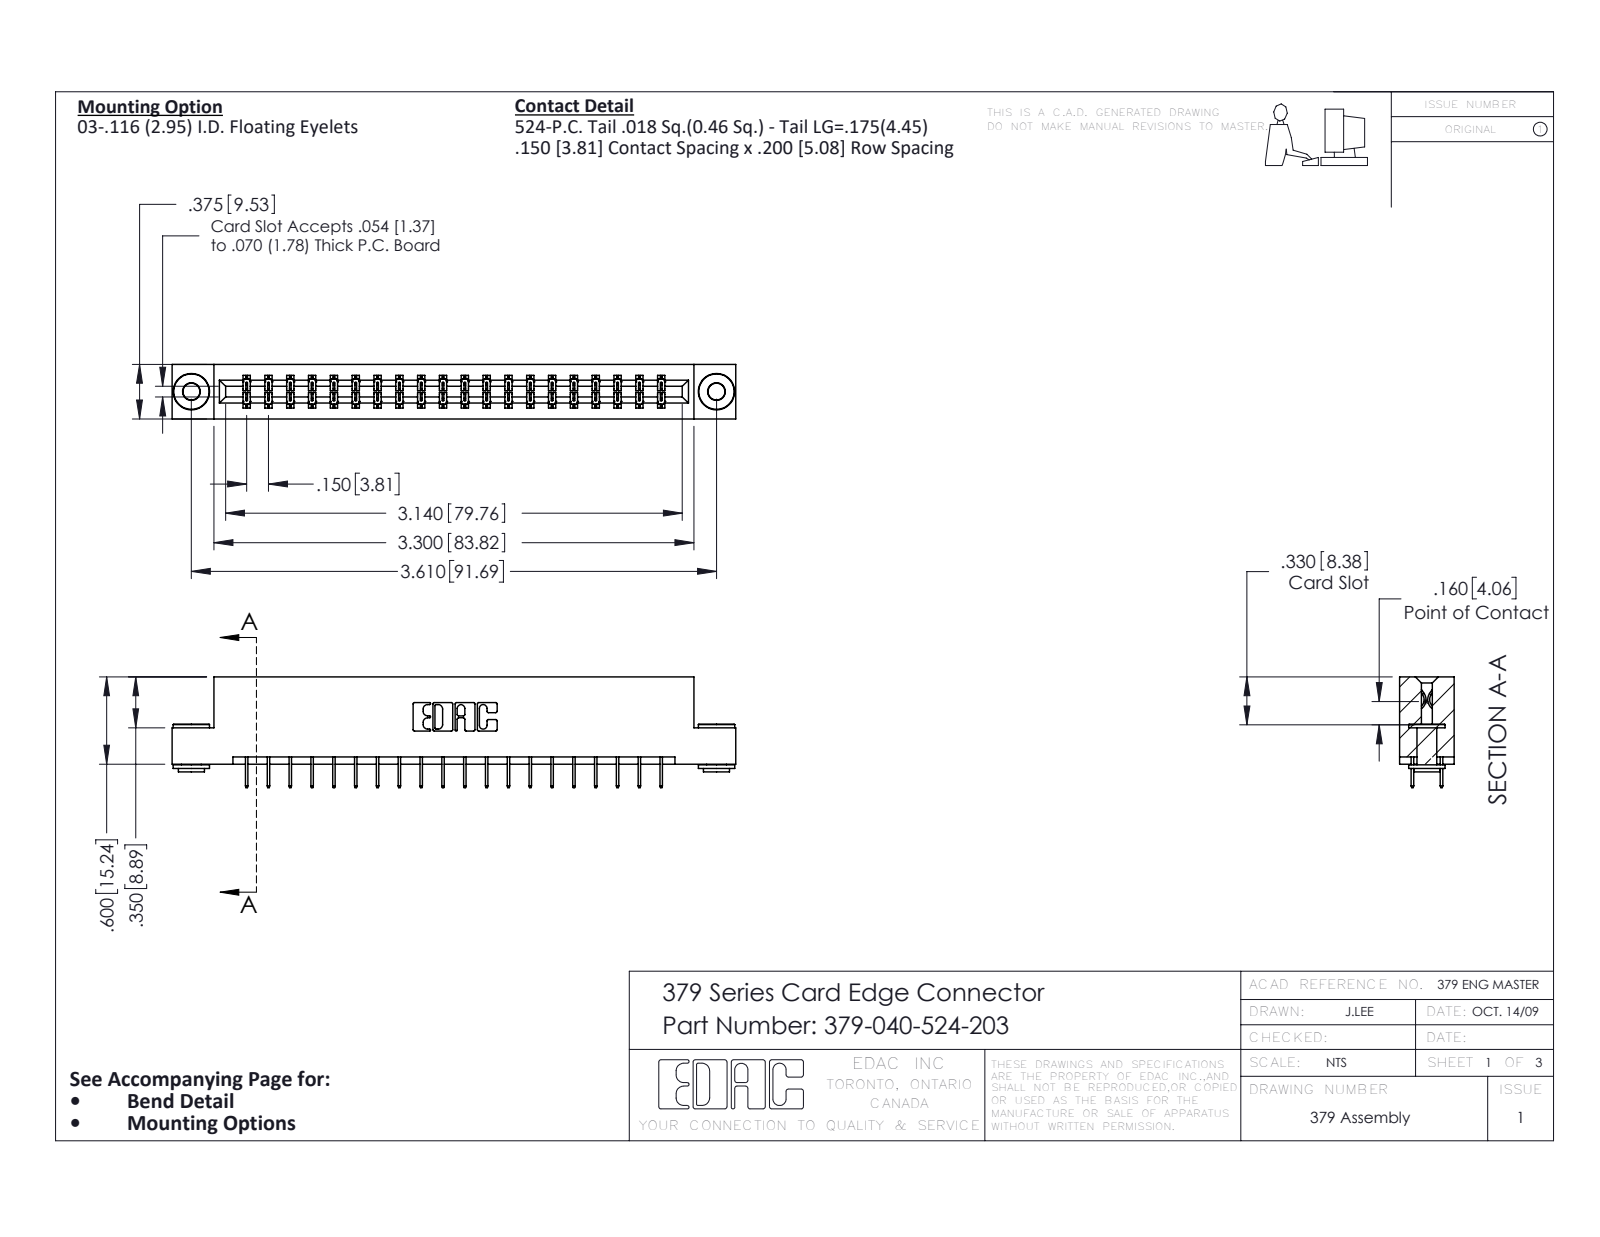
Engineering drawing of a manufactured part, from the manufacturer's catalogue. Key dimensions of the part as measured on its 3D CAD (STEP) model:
Part name (STEP PRODUCT): 345-250-002_345-250-002-102; 379 Part_Flush - .156 Dia - TH; 345-292-001_345-293-124; 379-040-524-203
STEP written by: SolidWorks 2016 (CONFIG_CONTROL_DESIGN)
Units: inches
Bodies: 43 solids, 2392 faces (1760 planar, 624 cylindrical, 8 other)
Overall size (bounding box): 3.875 × 0.762 × 0.375
Volume: 0.621 in³ · Surface area: 17.45 in²
Round holes (diameter × count): ⌀0.116 ×2, ⌀0.156 ×2
Round bosses / shafts (diameter × count): ⌀0.25 ×2, ⌀0.18 ×2, ⌀0.136 ×2
Partial cylindrical surfaces — rounded edges, fillets, slot ends (radius × count): R0.006 ×60, R0.01 ×22, R0.007 ×6, R0.031 ×6, R0.026 ×3, R0.014 ×2, R0.022 ×2, R0.024 ×2
Main face-to-face distances: 0.3, 0.375, 0.075, 0.2, 0.1, 0.225, 0.15, 0.05, 0.6, 0.55
Hole centre spacings: 3.61
